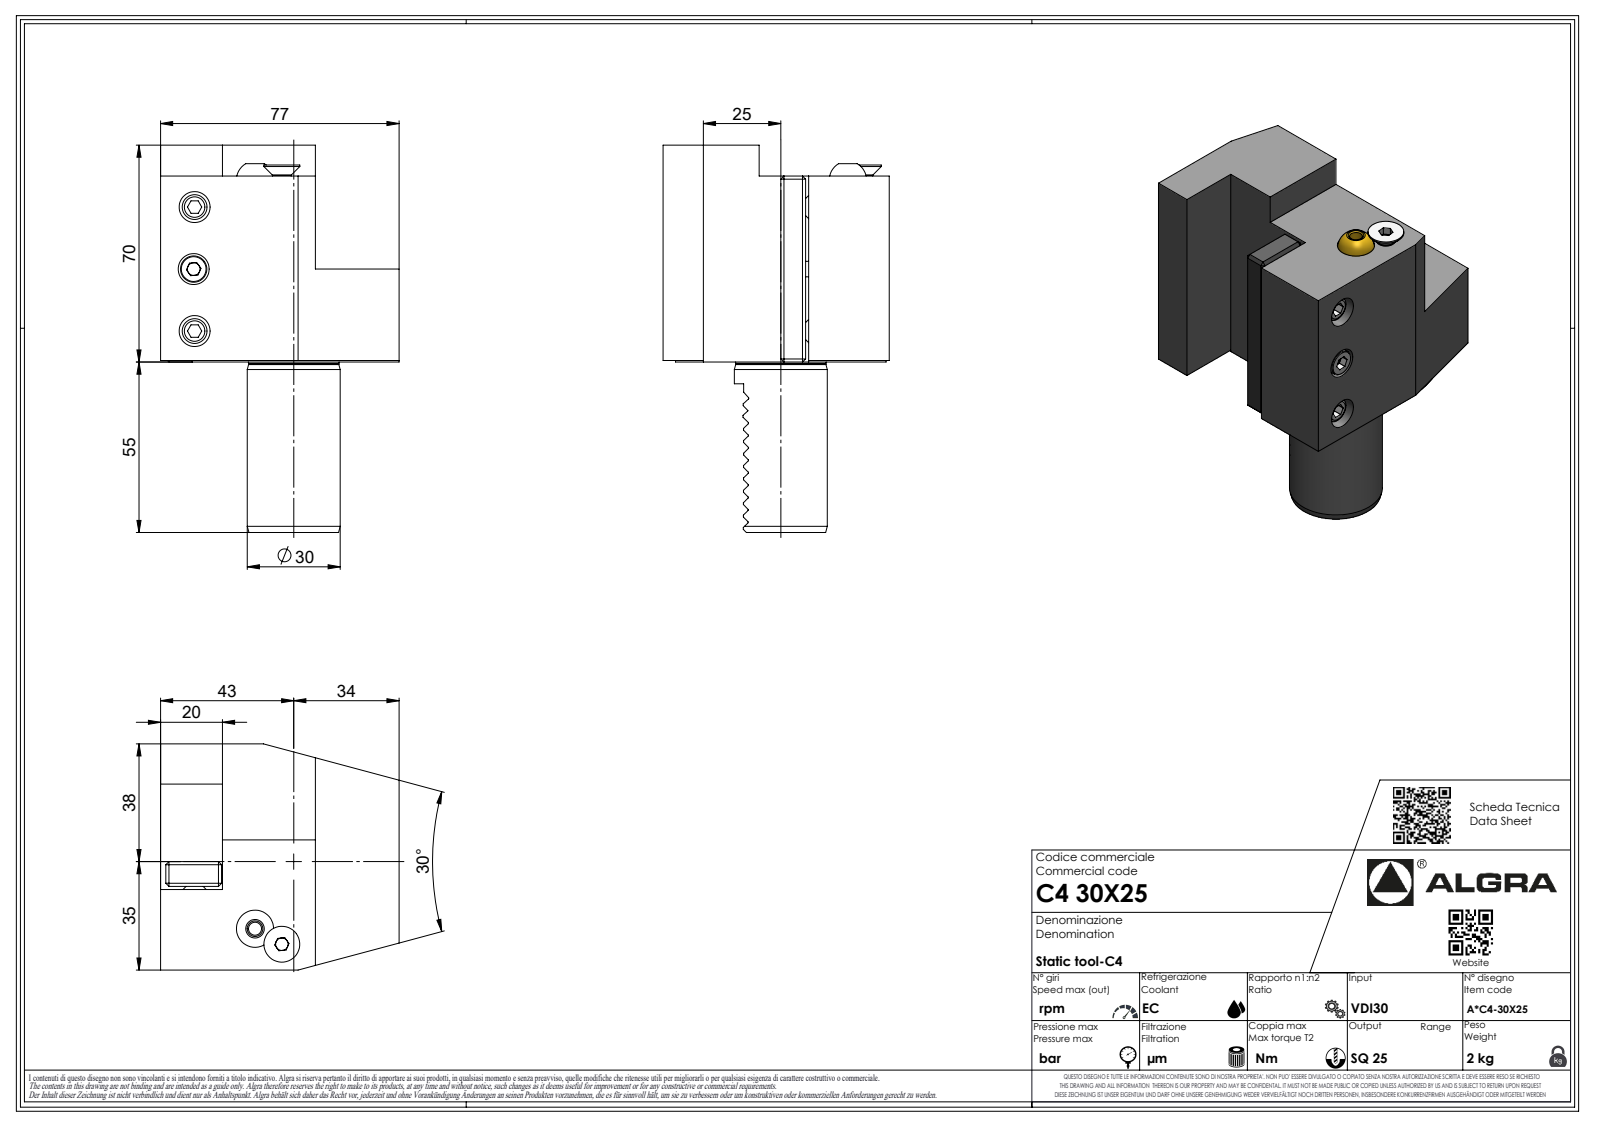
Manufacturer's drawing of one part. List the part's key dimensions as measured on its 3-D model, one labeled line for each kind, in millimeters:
Part name (STEP PRODUCT): C430X25
STEP written by: SolidWorks 2023 (AUTOMOTIVE_DESIGN)
Units: millimetres
Bodies: 1 solid, 321 faces (224 planar, 40 cylindrical, 57 other)
Overall size (bounding box): 125 × 77 × 73
Volume: 281 089 mm³ · Surface area: 35 768 mm²
Round holes (diameter × count): ⌀2.1 ×1
Round bosses / shafts (diameter × count): ⌀68 ×1, ⌀30 ×1, ⌀29.1 ×1, ⌀6.37 ×1, ⌀1.7 ×1
Partial cylindrical surfaces — rounded edges, fillets, slot ends (radius × count): R0.33 ×7, R0.52 ×7, R3.7 ×7, R0.3 ×3, R0.27 ×2, R0.21 ×1, R0.24 ×1, R0.26 ×1
Main face-to-face distances: 30, 60, 73, 50, 20, 77, 57, 27, 13, 0.5
